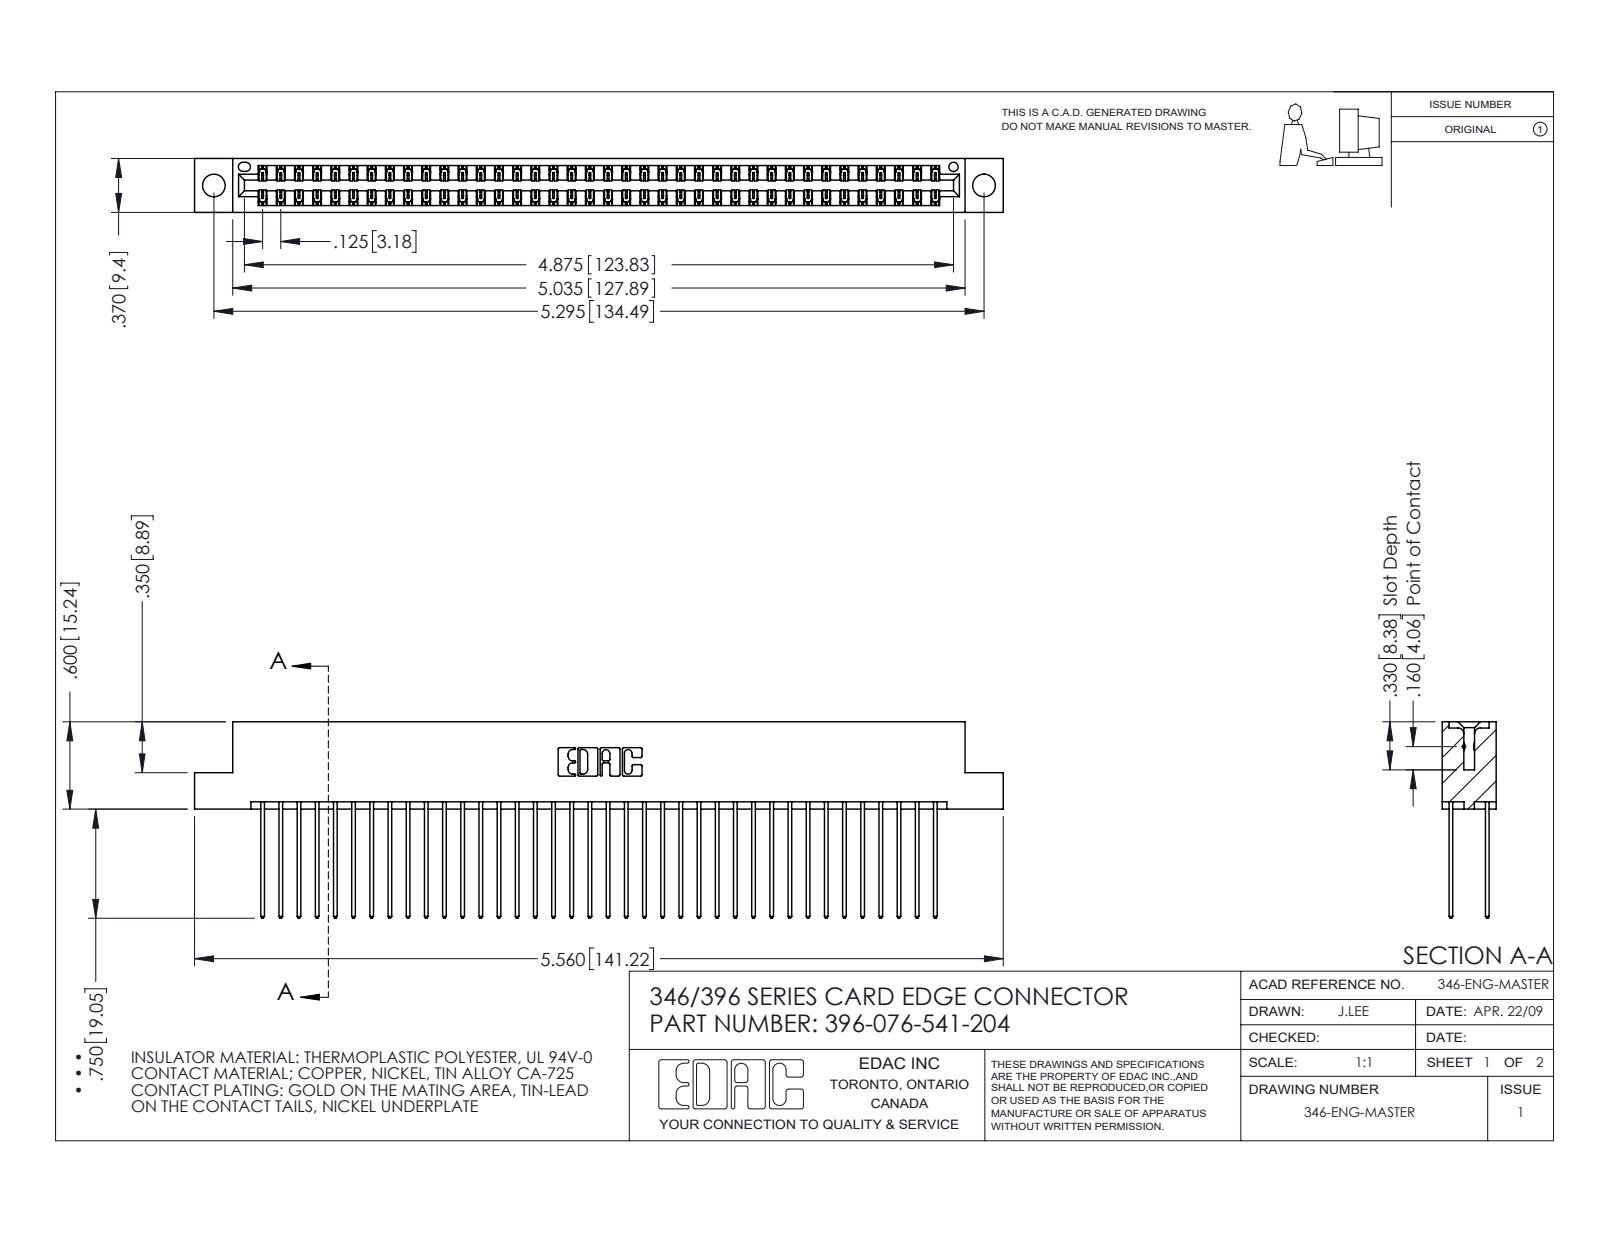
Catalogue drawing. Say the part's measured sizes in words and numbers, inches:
The part is named "396-076-541-204; 345-292-001_345-293-141; 346 Part_Flush Mounting Lugs - 0.156 Dia-TH". Its 3-D file was written by "SolidWorks 2016 (CONFIG_CONTROL_DESIGN)". It is 77 solids with 4074 faces: 2736 planar, 1338 cylindrical and 0 other. Overall it measures 5.56 by 1.35 by 0.37 inches. Its volume is 0.86 cubic inches and its surface area 32.87 square inches. Round holes: 2 of diameter 0.156, 1 of diameter 0.064. Partial cylindrical surfaces (rounded edges, fillets, slot ends): 114 of radius 0.006, 76 of radius 0.01, 22 of radius 0.01, 6 of radius 0.007, 6 of radius 0.031, 3 of radius 0.026, 2 of radius 0.014, 2 of radius 0.022. The main face-to-face distances are 0.048, 0.322, 0.25, 0.072, 0.298, 0.025, 0.37, 0.275, 0.225, 0.148. The hole center spacings are 0.246, 5.086, 5.295.
